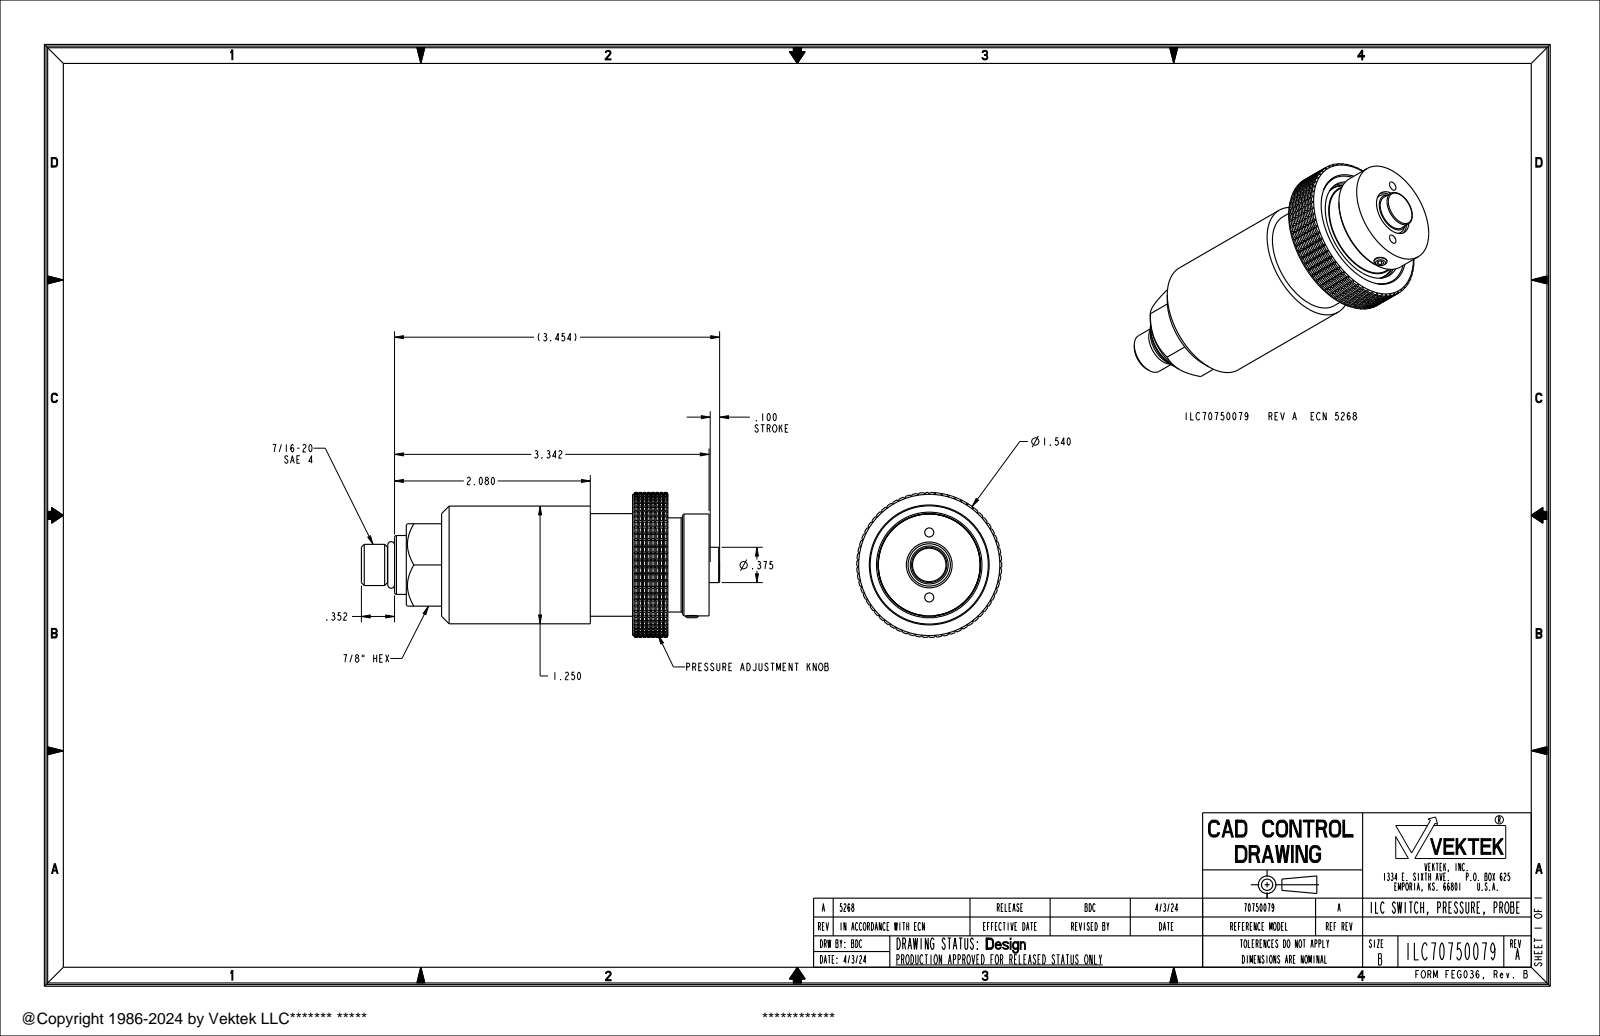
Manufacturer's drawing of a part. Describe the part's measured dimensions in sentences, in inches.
The part is named "ILC70750079". Its 3-D file was written by "CREO PARAMETRIC BY PTC INC, 2021164 (AUTOMOTIVE_DESIGN)". It is 0 solids with 2733 faces: 1085 planar, 556 cylindrical and 1092 other. Overall it measures 3.806 by 1.54 by 1.54 inches. Round holes: 2 of diameter 0.096, 1 of diameter 0.487, 1 of diameter 1.12. Round bosses or shafts: 1 of diameter 1.5, 1 of diameter 1.25, 1 of diameter 1.09, 1 of diameter 1.082, 1 of diameter 1, 1 of diameter 0.625, 1 of diameter 0.437, 1 of diameter 0.375. Partial cylindrical surfaces (rounded edges, fillets, slot ends): 1 of radius 0.77. The main face-to-face distances are 0.813, 0.875, 0.301, 0.512, 0.375, 0.074, 0.438, 0.449, 0.75, 0.824. The hole center spacings are 0.345, 0.69.
